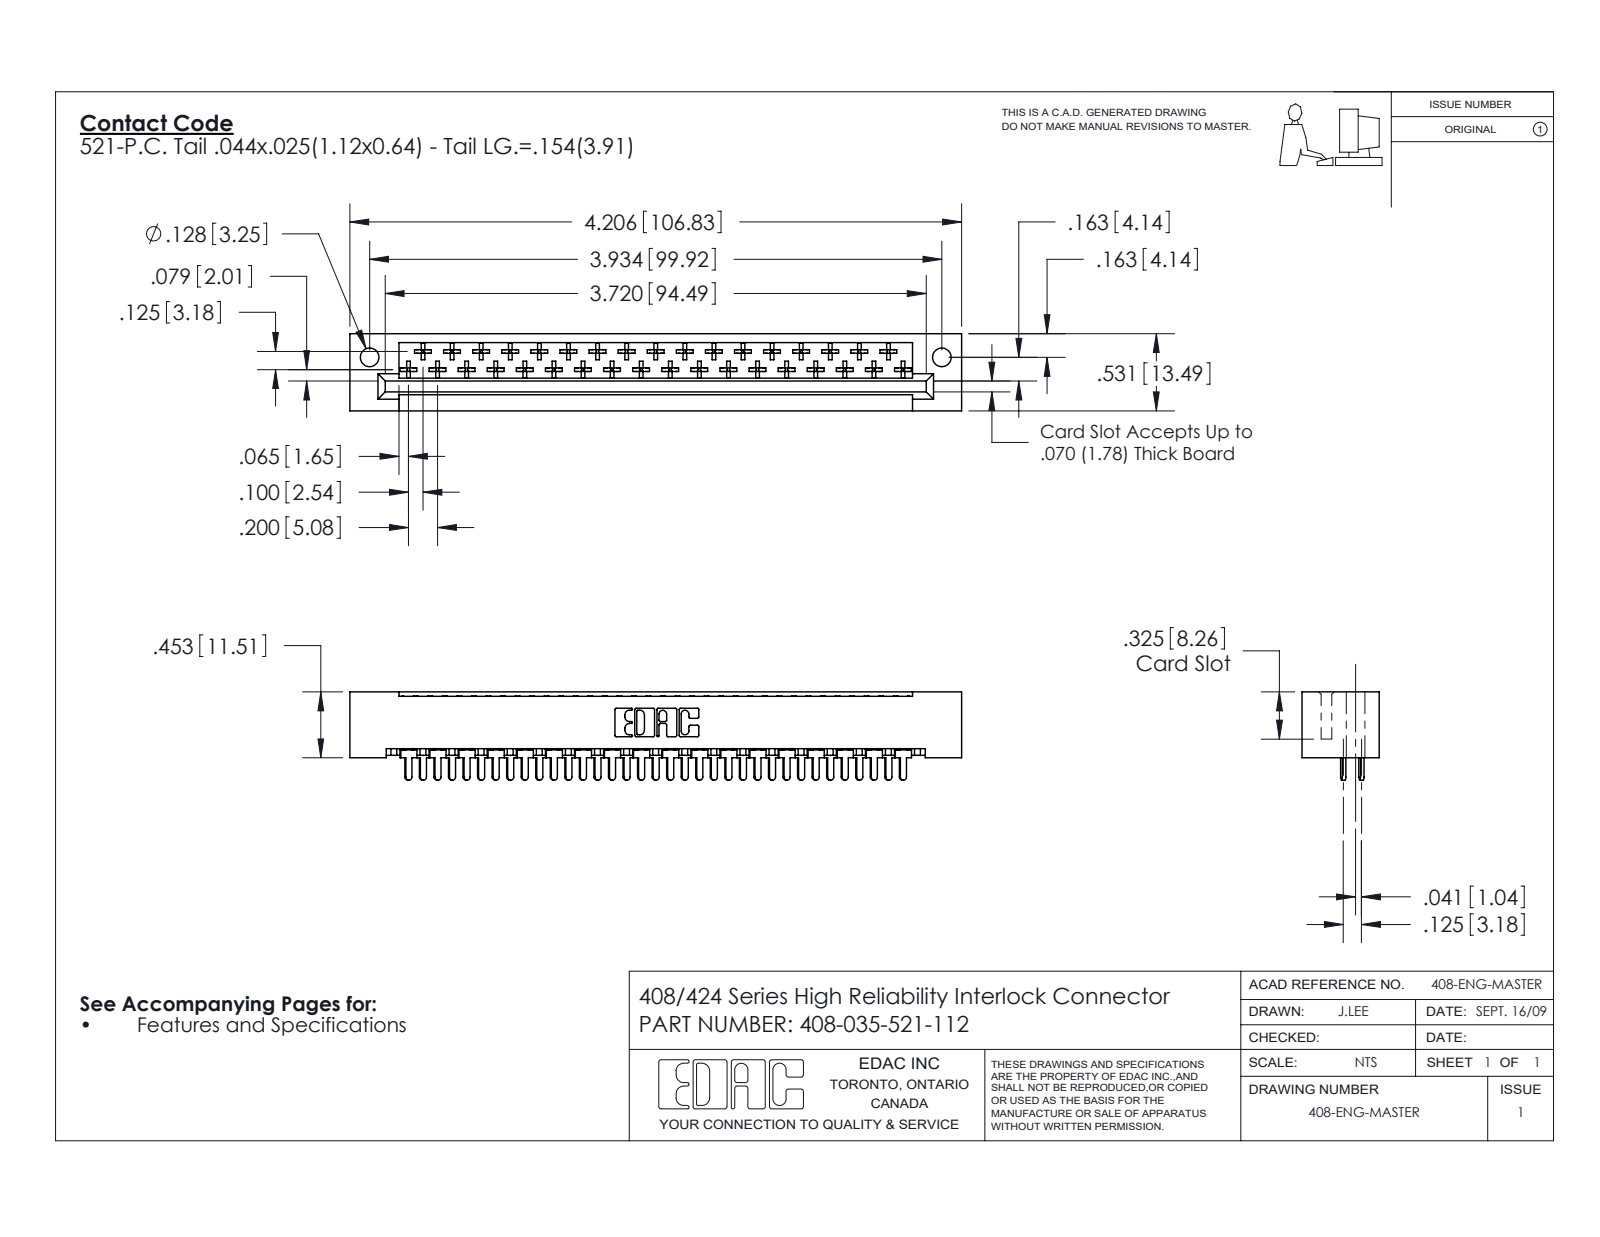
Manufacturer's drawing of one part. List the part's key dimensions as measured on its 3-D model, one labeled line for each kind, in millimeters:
Part name (STEP PRODUCT): 408 Part_035 - 1; 408-290-001_408-290-121; 408-035-521-112
STEP written by: SolidWorks 2016 (CONFIG_CONTROL_DESIGN)
Units: millimetres
Bodies: 36 solids, 2052 faces (1549 planar, 363 cylindrical, 140 other)
Overall size (bounding box): 106.8 × 15.4 × 13.5
Volume: 12 200 mm³ · Surface area: 14 510 mm²
Round holes (diameter × count): ⌀3.3 ×2
Partial cylindrical surfaces — rounded edges, fillets, slot ends (radius × count): R0.3 ×210, R0.5 ×37, R0.6 ×35, R0.3 ×22, R0.2 ×6, R0.8 ×6, R0.7 ×3
Main face-to-face distances: 13.5, 0.6, 2.5, 3.2, 0.6, 10.2, 6.9, 6, 6.6, 7.5
Hole centre spacings: 99.9
